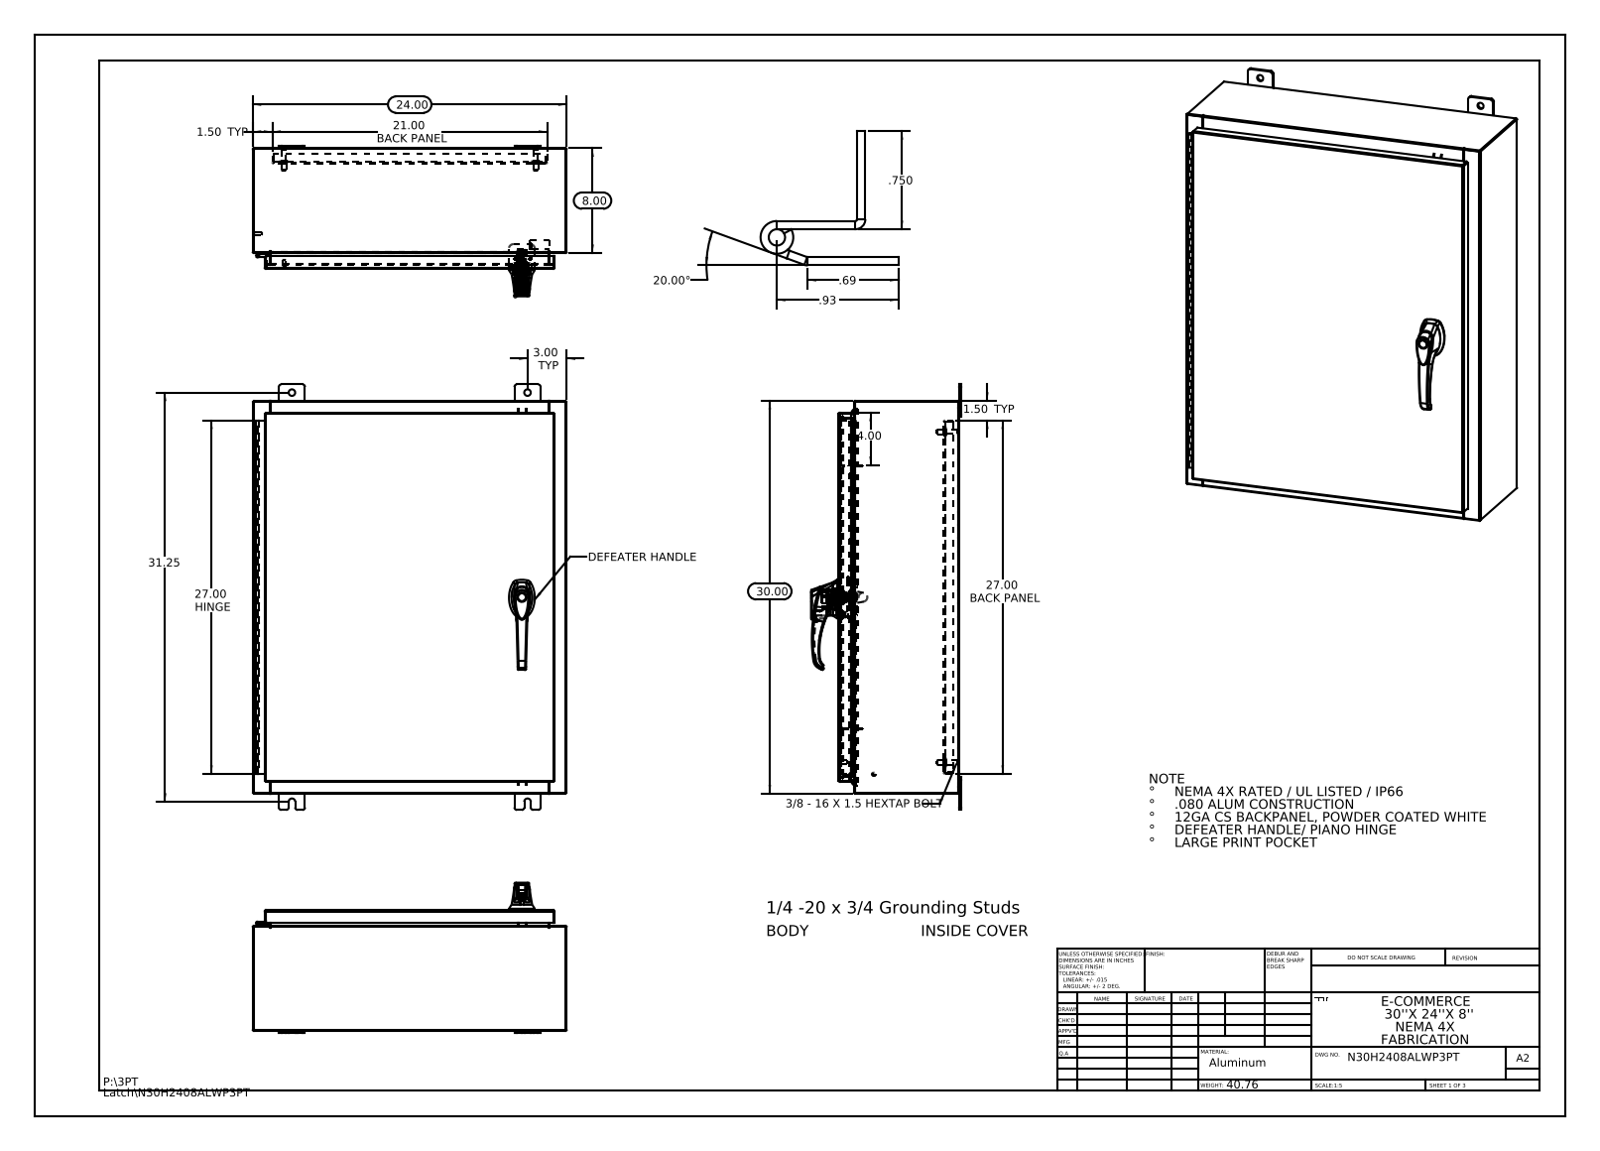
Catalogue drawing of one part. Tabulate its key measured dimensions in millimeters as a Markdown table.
| quantity | value |
| --- | --- |
| part name | 26161102; g26103103_26163303; 21130102; N30H2408ALWP3PT (+8 more) |
| STEP written by | SolidWorks 2013 (CONFIG_CONTROL_DESIGN) |
| units | millimeters |
| bodies | 37 solids, 2662 faces (971 planar, 993 cylindrical, 698 other) |
| overall size | 825.5 × 609.6 × 292 |
| volume | 4 461 000 mm³ |
| surface area | 4 332 000 mm² |
| round holes (diameter × count) | 12.7 × 8, 6.4 × 4, 3.5 × 3, 4.1 × 3, 2 × 2, 5.2 × 2, 8 × 2, 11.1 × 2, 3.2 × 1, 3.2 × 1, 5 × 1, 7 × 1 |
| round bosses / shafts (diameter × count) | 15.9 × 4, 9.5 × 4, 8.4 × 4, 4 × 4, 3.6 × 4, 8 × 3, 6 × 3, 30 × 1 |
| partial cylindrical surfaces (radius × count) | 3 × 37, 0.2 × 33, 0.3 × 24, 4.8 × 24, 2.2 × 18, 1 × 15, 0.7 × 12, 0.2 × 6 |
| main face-to-face distances | 1.9, 231.8, 2.6, 229.9, 233.7, 25.4, 27.3, 204.5, 206.4, 29.9 |
| hole center spacings | 212.6, 7.5, 15.9, 21.4, 31.8, 33.4, 39.6, 47.2 |
